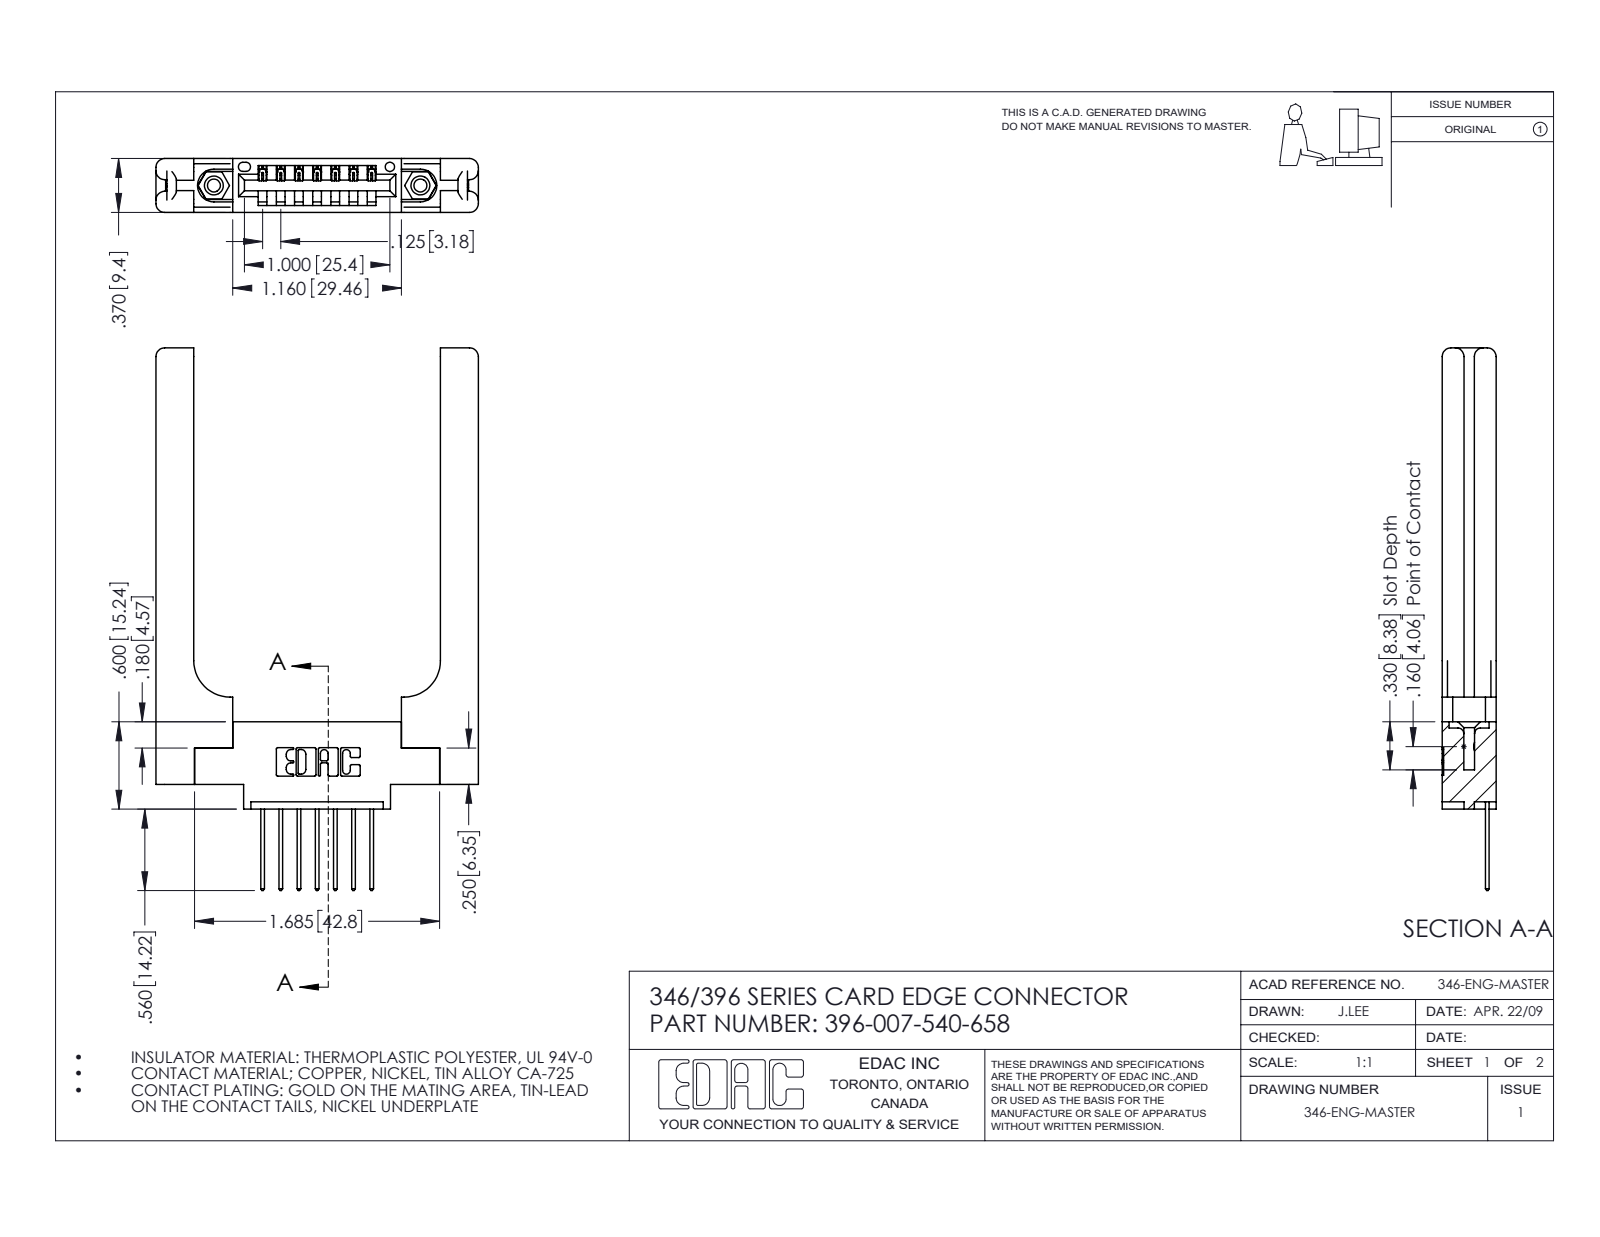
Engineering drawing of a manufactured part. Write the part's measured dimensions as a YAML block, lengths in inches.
part_name: "346-220-058_345-220-058; 346 Part_0.170 Offset - 0.156 Dia-TH; 345-250-001_345-250-001-102; 396-007-540-658 (+1 more)"
step_written_by: "SolidWorks 2016 (CONFIG_CONTROL_DESIGN)"
units: inches
bodies: {solids: 12, faces: 788, planar: 508, cylindrical: 220, other: 60}
overall_size: [3.73, 2.216, 0.37]
volume: 0.764
surface_area: 17.47
round_holes:
  - {diameter: 0.089, count: 2}
  - {diameter: 0.125, count: 2}
  - {diameter: 0.156, count: 2}
  - {diameter: 0.064, count: 1}
round_bosses_or_shafts:
  - {diameter: 0.155, count: 2}
partial_cylinders:
  - {radius: 0.01, count: 22}
  - {radius: 0.06, count: 16}
  - {radius: 0.006, count: 14}
  - {radius: 0.01, count: 14}
  - {radius: 0.007, count: 6}
  - {radius: 0.031, count: 6}
  - {radius: 0.026, count: 3}
  - {radius: 0.03, count: 2}
face_to_face_distances: [0.37, 0.15, 0.22, 0.072, 0.148, 0.25, 0.102, 1.696, 0.048, 0.322]
hole_center_spacings: [0.246, 1.217, 1.42]
